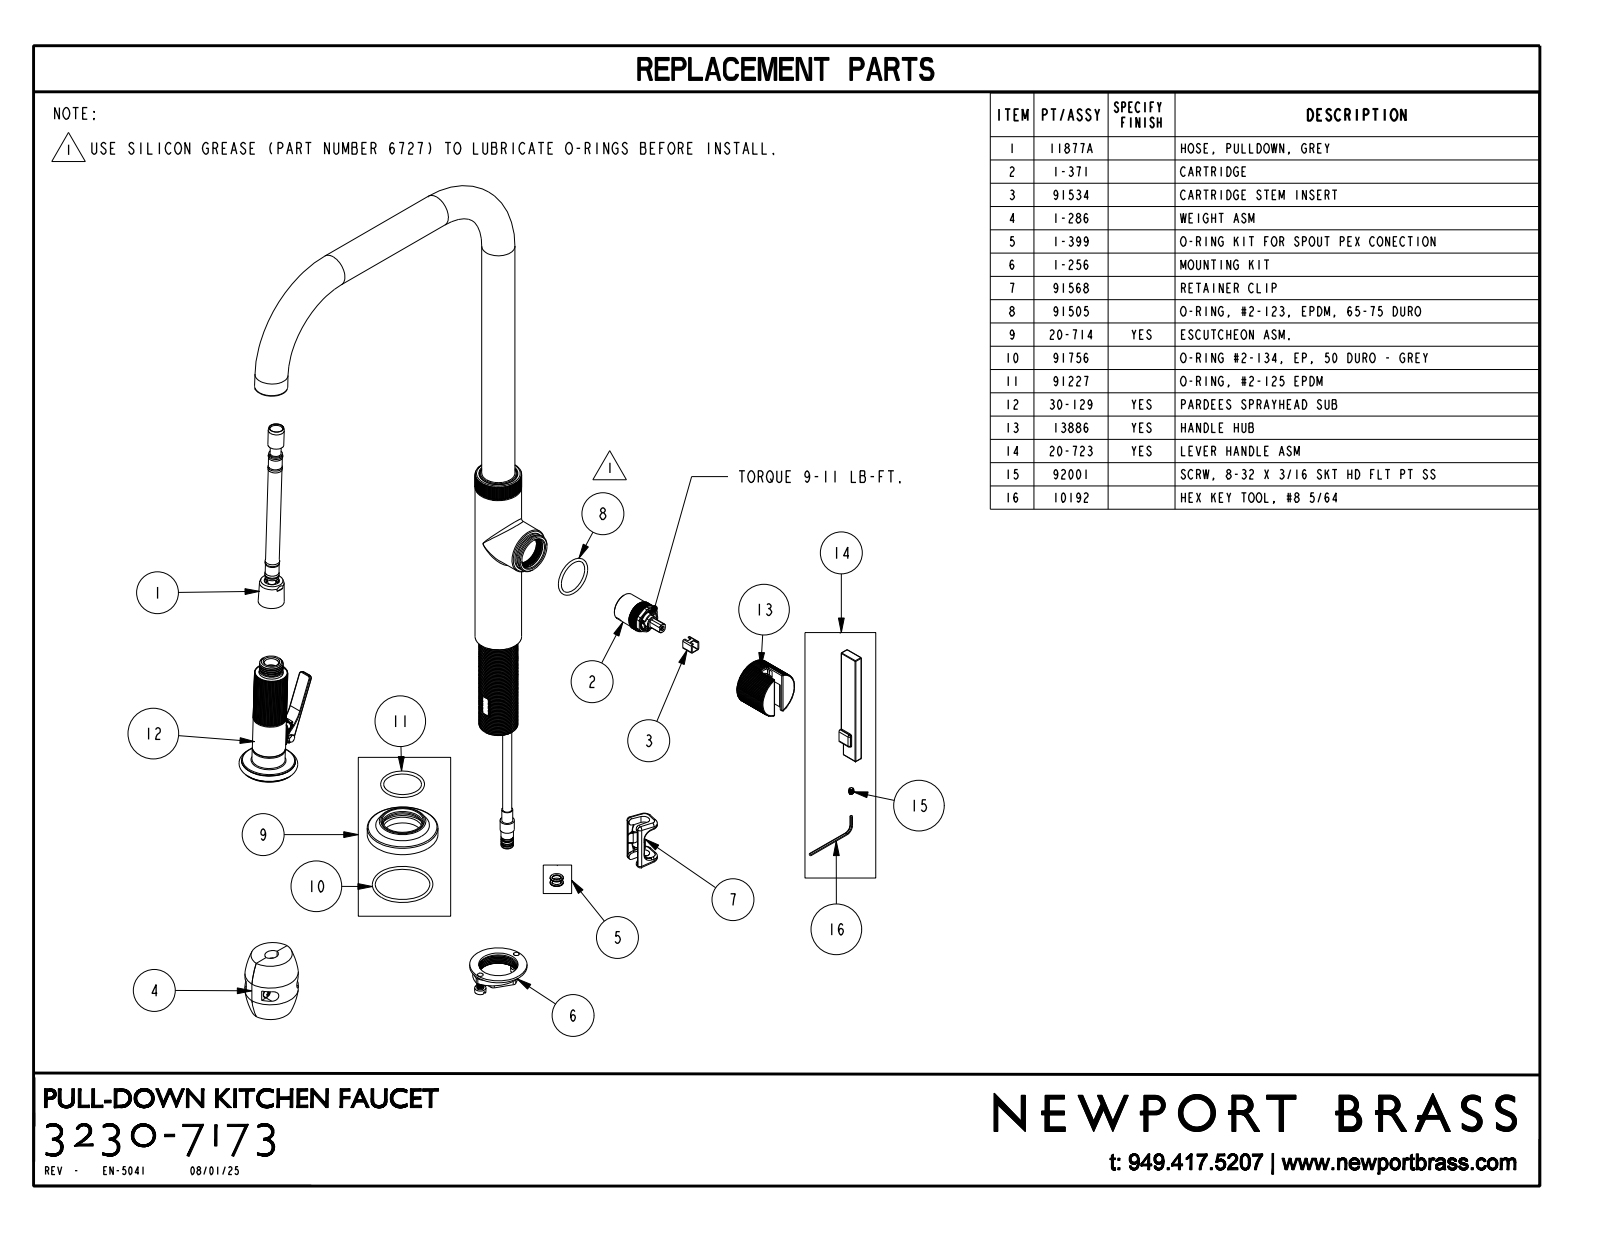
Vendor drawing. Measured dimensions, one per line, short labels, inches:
name: 3230-7173
written by: CREO PARAMETRIC BY PTC INC, 2025093 (CONFIG_CONTROL_DESIGN)
unit: in
bodies: 5 solids, 1329 faces (649 planar, 462 cylindrical, 218 other)
size: 20.54 × 13.403 × 3.972
volume: 49.77 in³; area: 188.1 in²
holes: 1× ⌀0.228, 1× ⌀1.035
bosses: 18× ⌀0.102, 1× ⌀2.43, 1× ⌀1.855, 1× ⌀1.6, 1× ⌀1.354, 1× ⌀1.142, 1× ⌀1.14, 1× ⌀0.937
rounds: 45× R0.02, 23× R0.03, 23× R0.06, 5× R0.025, 4× R0.045, 4× R0.13, 3× R0.1, 2× R0.05
face distances: 0.3, 0.43, 7.41, 0.713, 0.308, 0.025, 0.13, 0.1, 0.7, 0.7
